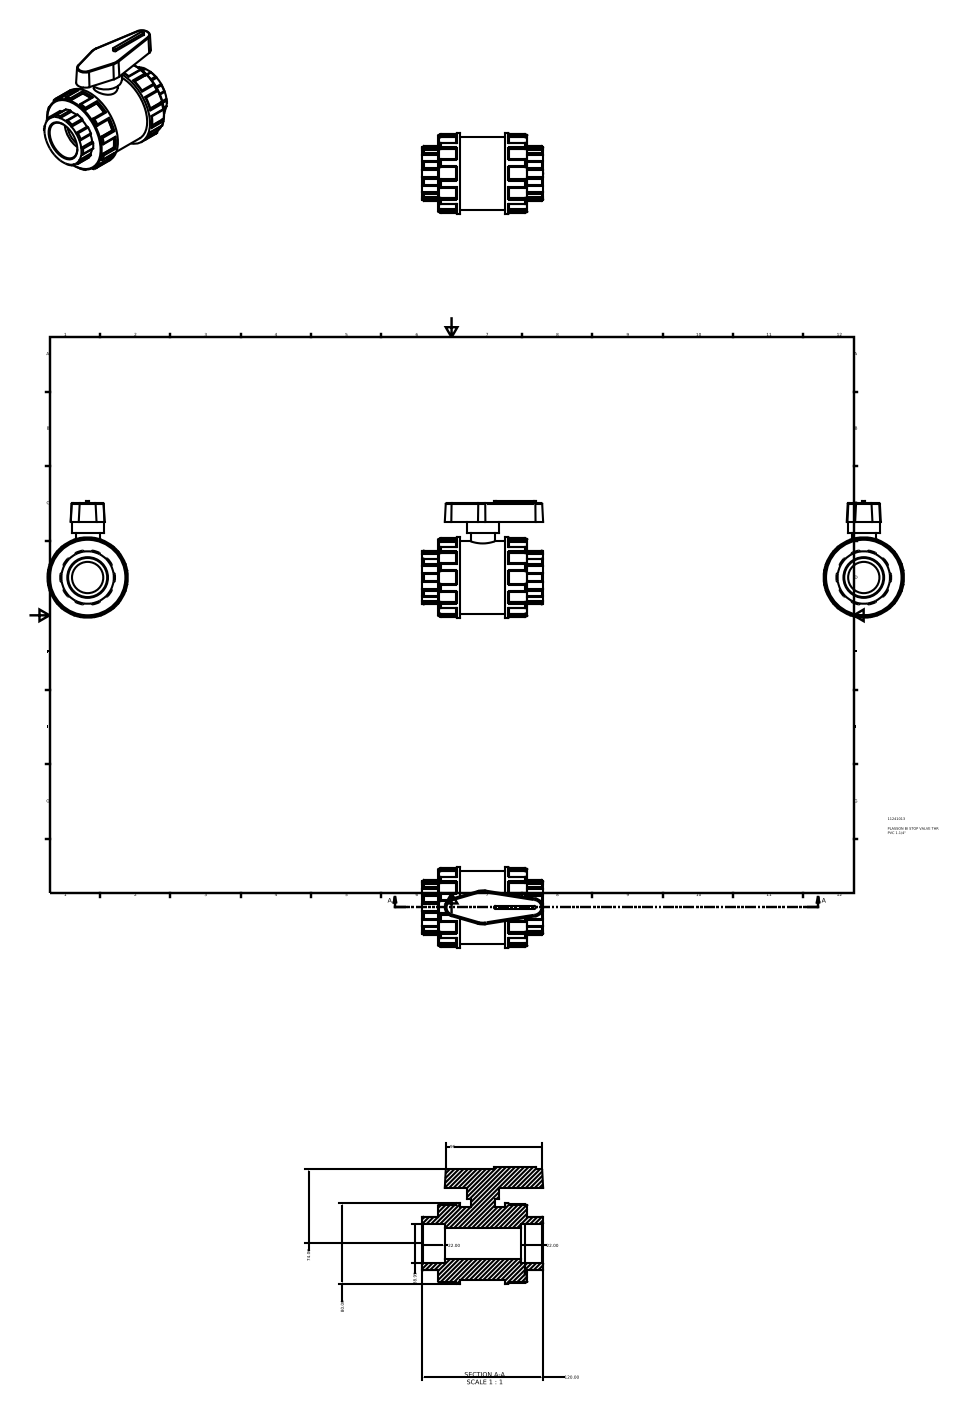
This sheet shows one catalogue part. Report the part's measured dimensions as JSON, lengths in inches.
{"part_name": "11241013", "step_written_by": "Autodesk Inventor 2015 (AUTOMOTIVE_DESIGN)", "units": "inches", "bodies": {"solids": 1, "faces": 434, "planar": 114, "cylindrical": 192, "other": 128}, "overall_size": [4.731, 4.576, 3.15], "volume_in3": 24.98, "surface_area_in2": 92.55, "round_holes": [[1.227, 1], [1.533, 1]], "round_bosses_or_shafts": [[3.15, 1], [3.024, 1], [2.835, 1], [1.26, 1], [0.945, 1]], "partial_cylinders_radius": [[0.046, 76], [0.031, 4], [0.063, 2], [1.028, 1], [1.074, 1]], "face_to_face_distances": [0.866, 0.606, 3.252, 3.512, 2.646, 1.472, 4.118, 0.728, 1.78, 3.858]}
